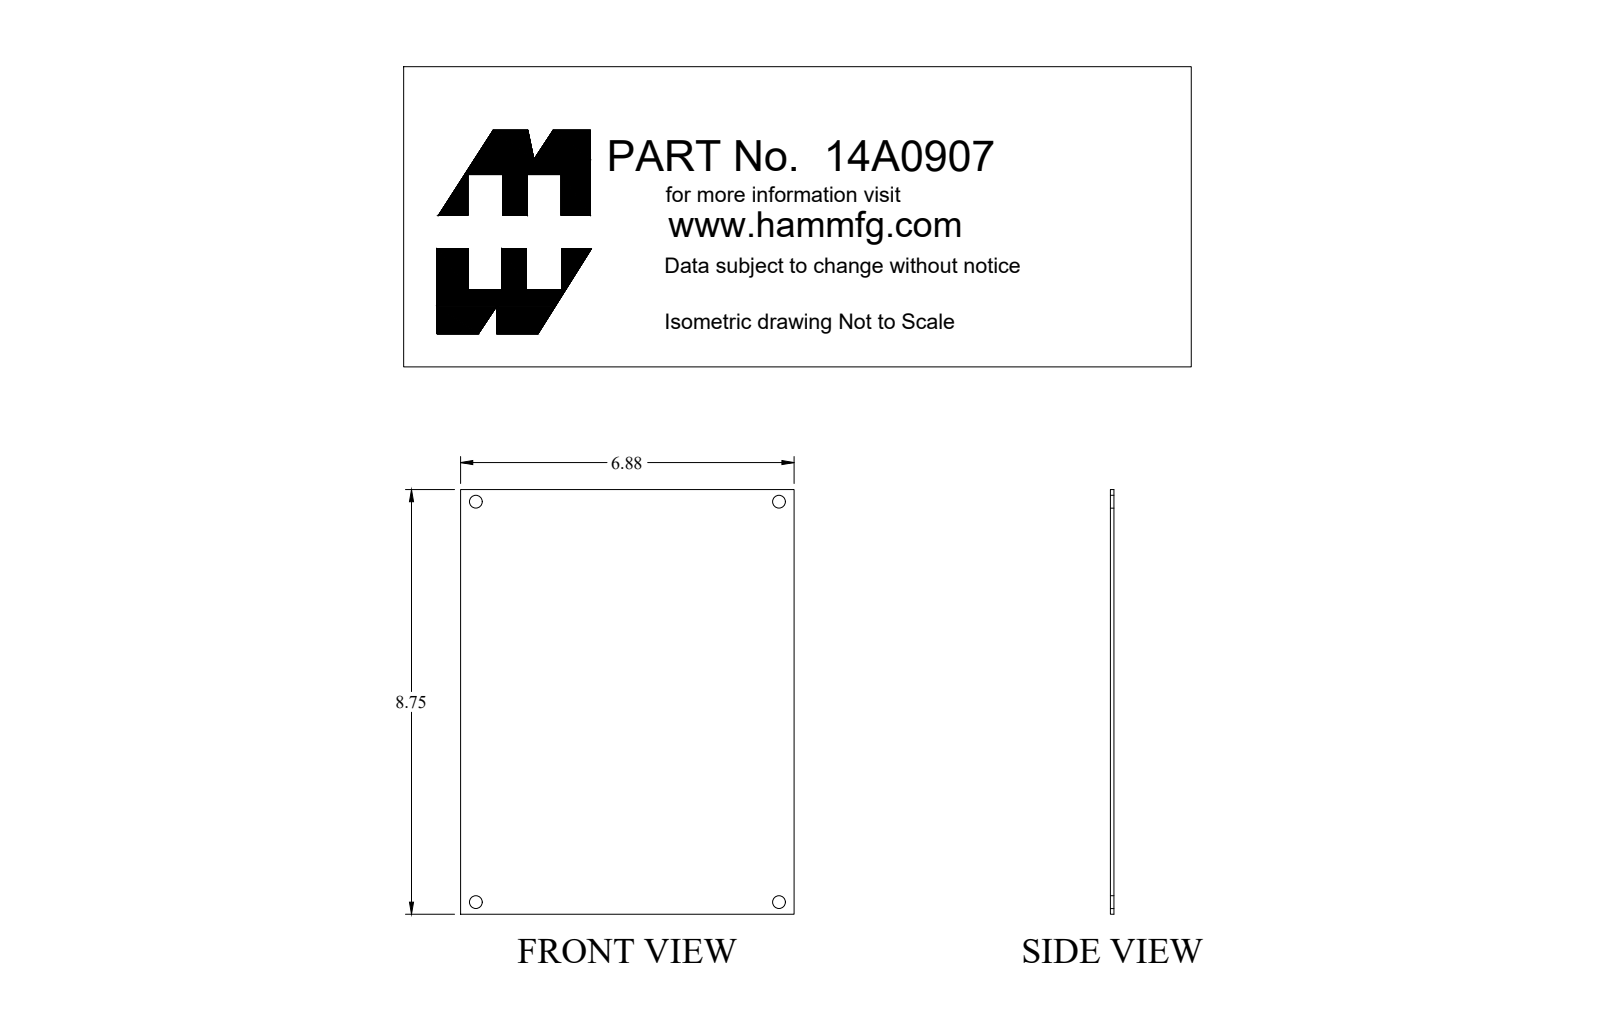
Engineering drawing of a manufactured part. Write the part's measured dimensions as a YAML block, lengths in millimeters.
part_name: "14A0907"
step_written_by: "SolidWorks 2018 (AUTOMOTIVE_DESIGN)"
units: millimeters
bodies: {solids: 1, faces: 10, planar: 6, cylindrical: 4, other: 0}
overall_size: [222.3, 174.6, 1.8]
volume: 70710
surface_area: 78970
round_holes:
  - {diameter: 6.7, count: 4}
face_to_face_distances: [1.8, 174.6, 222.3]
hole_center_spacings: [158.8, 209.6, 262.9]
